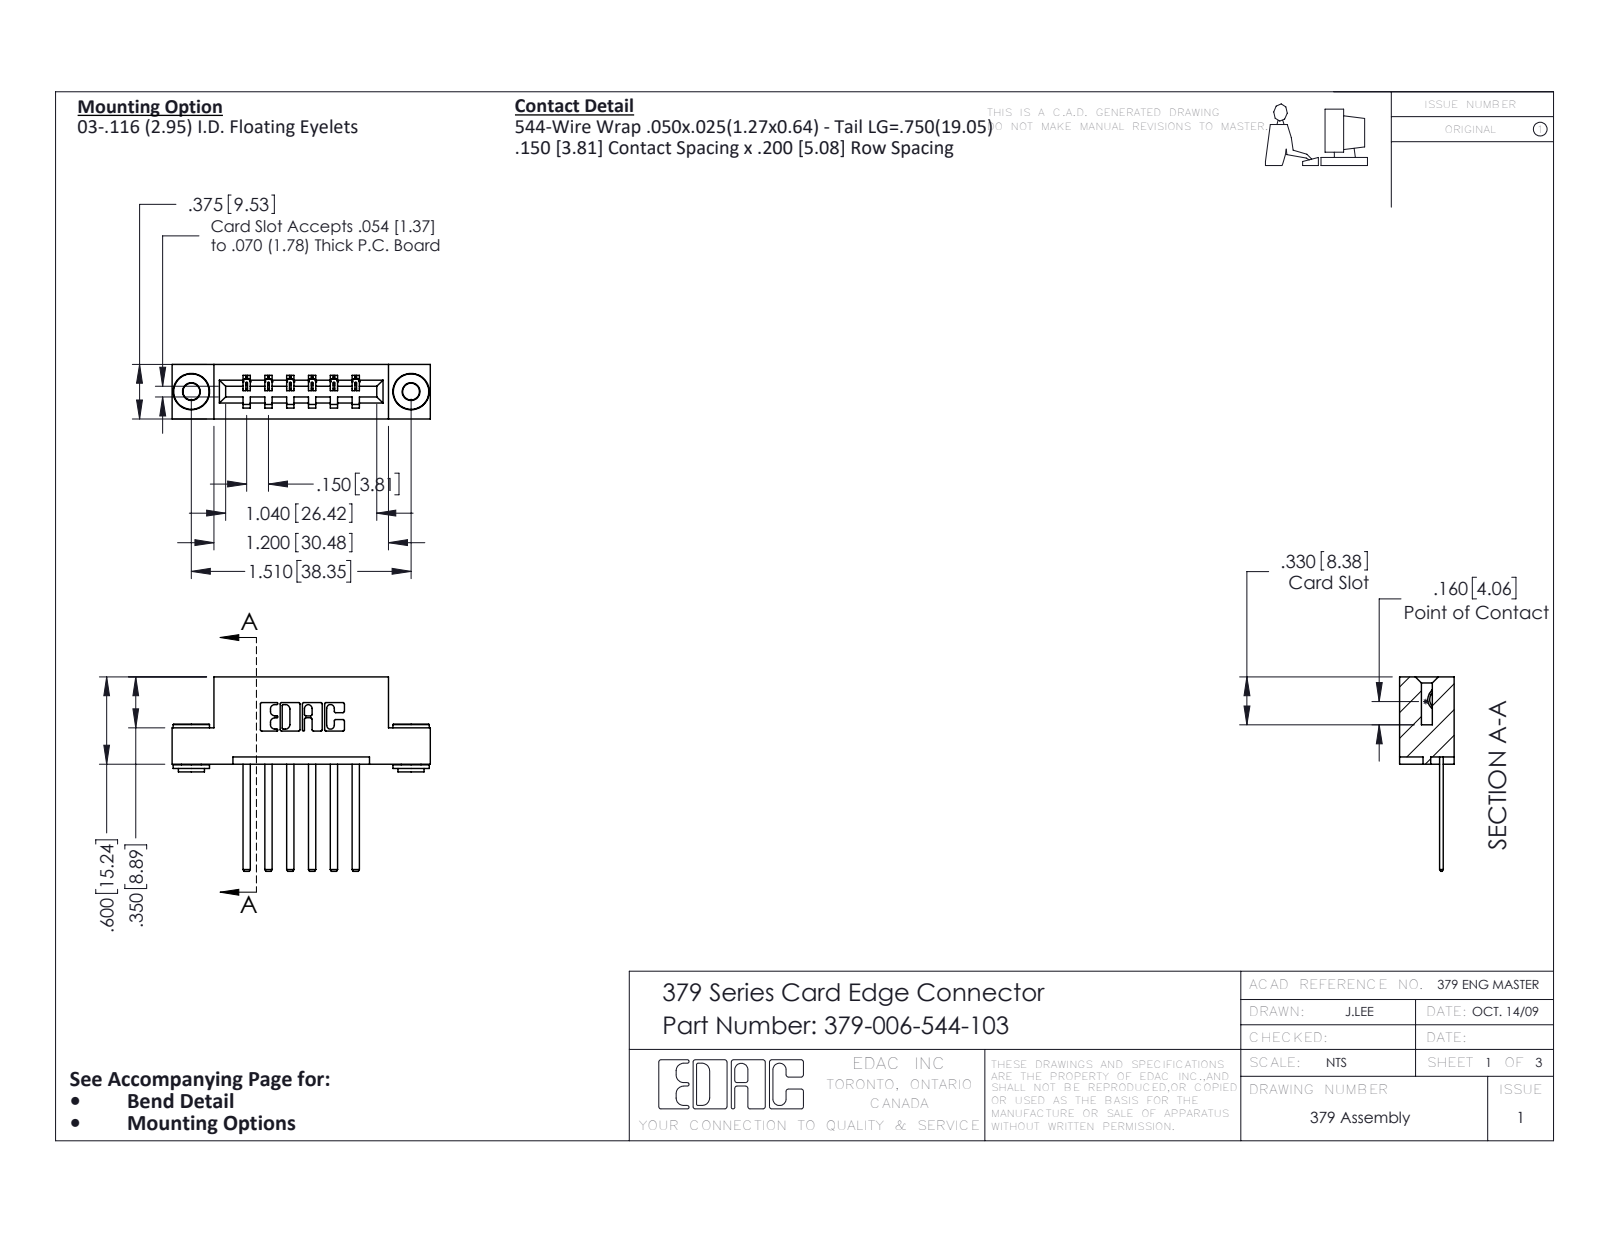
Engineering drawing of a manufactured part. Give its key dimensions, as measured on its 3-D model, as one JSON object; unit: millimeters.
{"part_name": "345-250-002_345-250-002-102; 345-292-001_345-293-144; 379-006-544-103; 379 Part_Flush - .156 Dia - TH", "step_written_by": "SolidWorks 2016 (CONFIG_CONTROL_DESIGN)", "units": "millimeters", "bodies": {"solids": 9, "faces": 464, "planar": 308, "cylindrical": 148, "other": 8}, "overall_size": [45.1, 34, 9.5], "volume_mm3": 4390, "surface_area_mm2": 4782, "round_holes": [[2.9, 2], [4, 2]], "round_bosses_or_shafts": [[6.4, 2], [4.6, 2], [3.5, 2]], "partial_cylinders_radius": [[0.3, 22], [0.2, 12], [0.2, 6], [0.8, 6], [0.7, 3], [0.4, 1], [0.6, 1], [0.6, 1]], "face_to_face_distances": [7.6, 5.1, 3.8, 2.5, 1.3, 1.9, 6.4, 8.9, 9.5, 15.2], "hole_center_spacings": [38.4]}
